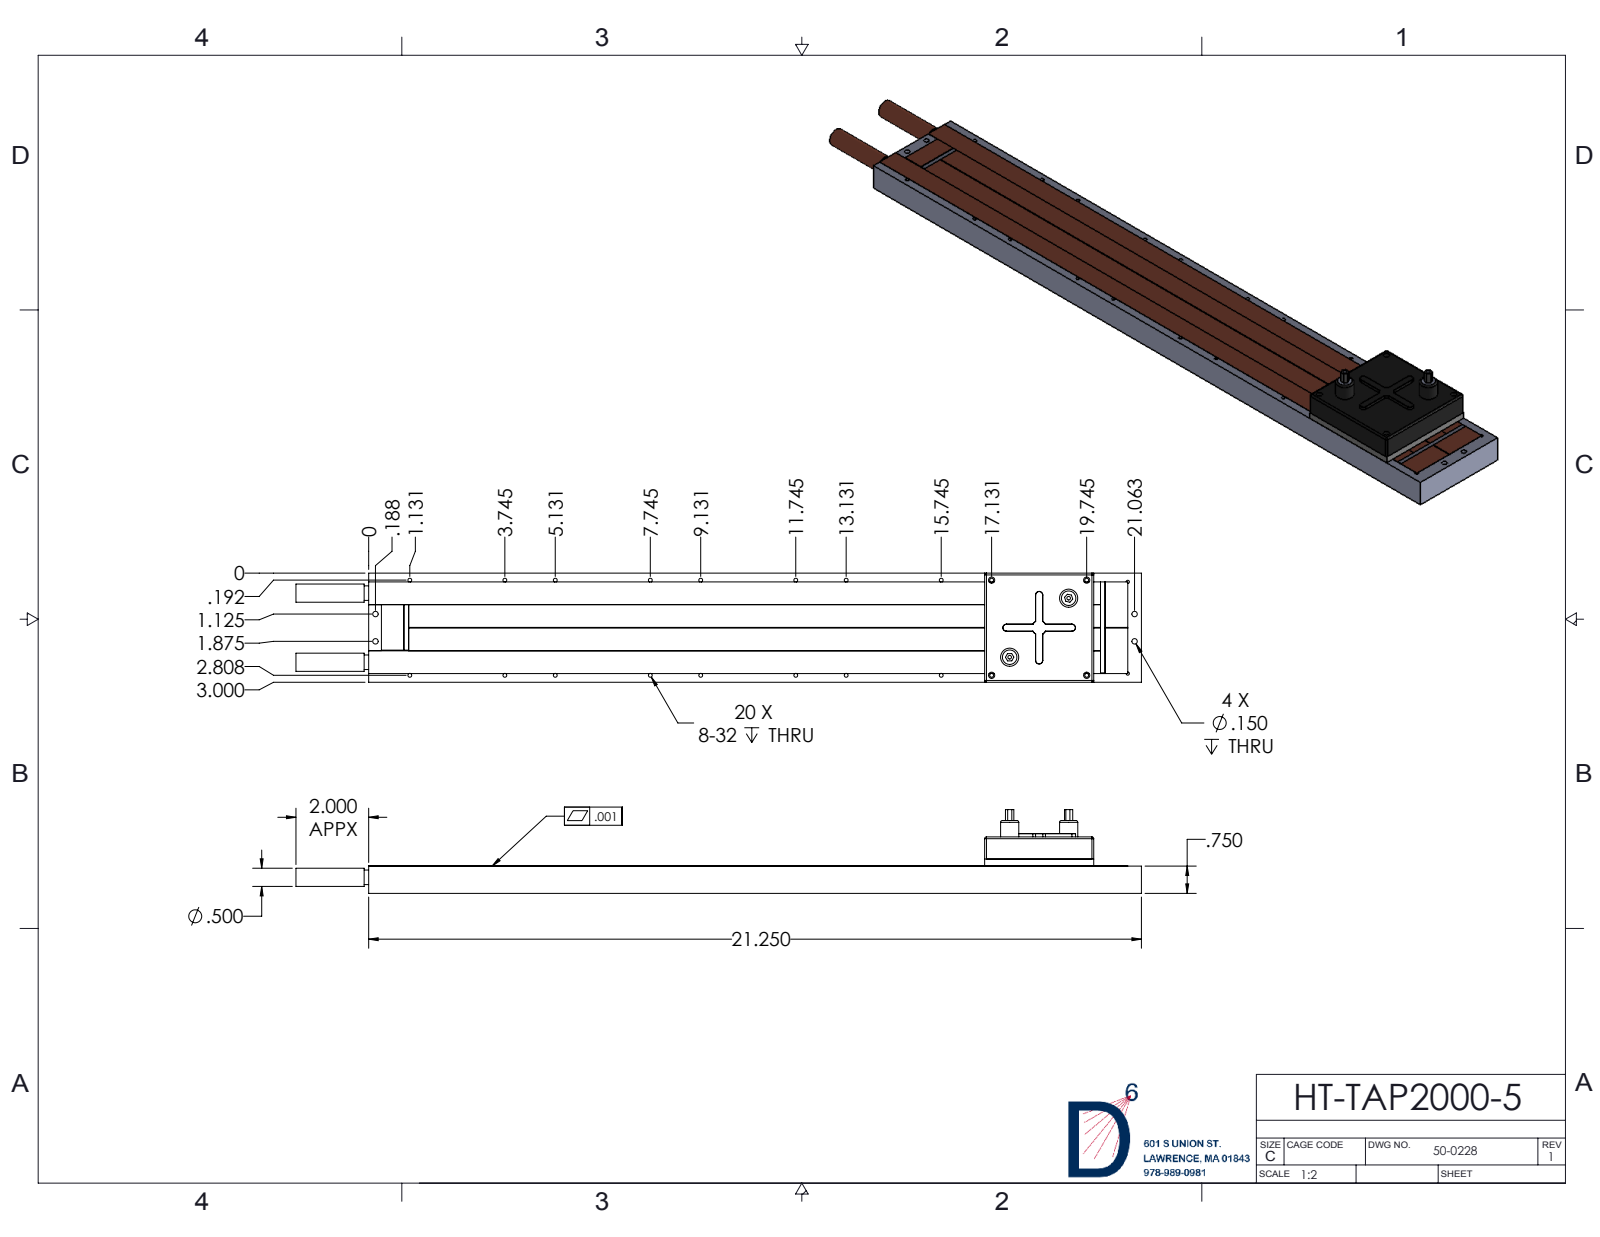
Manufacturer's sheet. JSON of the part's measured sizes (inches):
{"part_name": "TAP2000 RESISTOR; BP-TAP2000-5; HT-IN-OUT-ADAPTER-.4OD; HT-TAP2000-5 (+6 more)", "step_written_by": "SolidWorks 2013 (CONFIG_CONTROL_DESIGN)", "units": "inches", "bodies": {"solids": 16, "faces": 415, "planar": 233, "cylindrical": 165, "other": 17}, "overall_size": [23.25, 3, 2.303], "volume_in3": 43.69, "surface_area_in2": 600.3, "round_holes": [[0.136, 20], [0.3, 7], [0.15, 4], [0.172, 4], [0.1, 2], [0.32, 2], [0.4, 2], [0.402, 2], [0.504, 2]], "round_bosses_or_shafts": [[0.5, 4], [0.4, 2]], "partial_cylinders_radius": [[0.05, 8], [0.005, 4], [0.1, 4], [0.045, 2], [0.2, 1]], "face_to_face_distances": [0.5, 0.625, 0.125, 1.895, 0.13, 0.625, 0.755, 0.375, 0.75, 1.27], "hole_center_spacings": [4, 4.78, 8, 8.417, 2.614, 2.616, 3.698, 1.386]}
